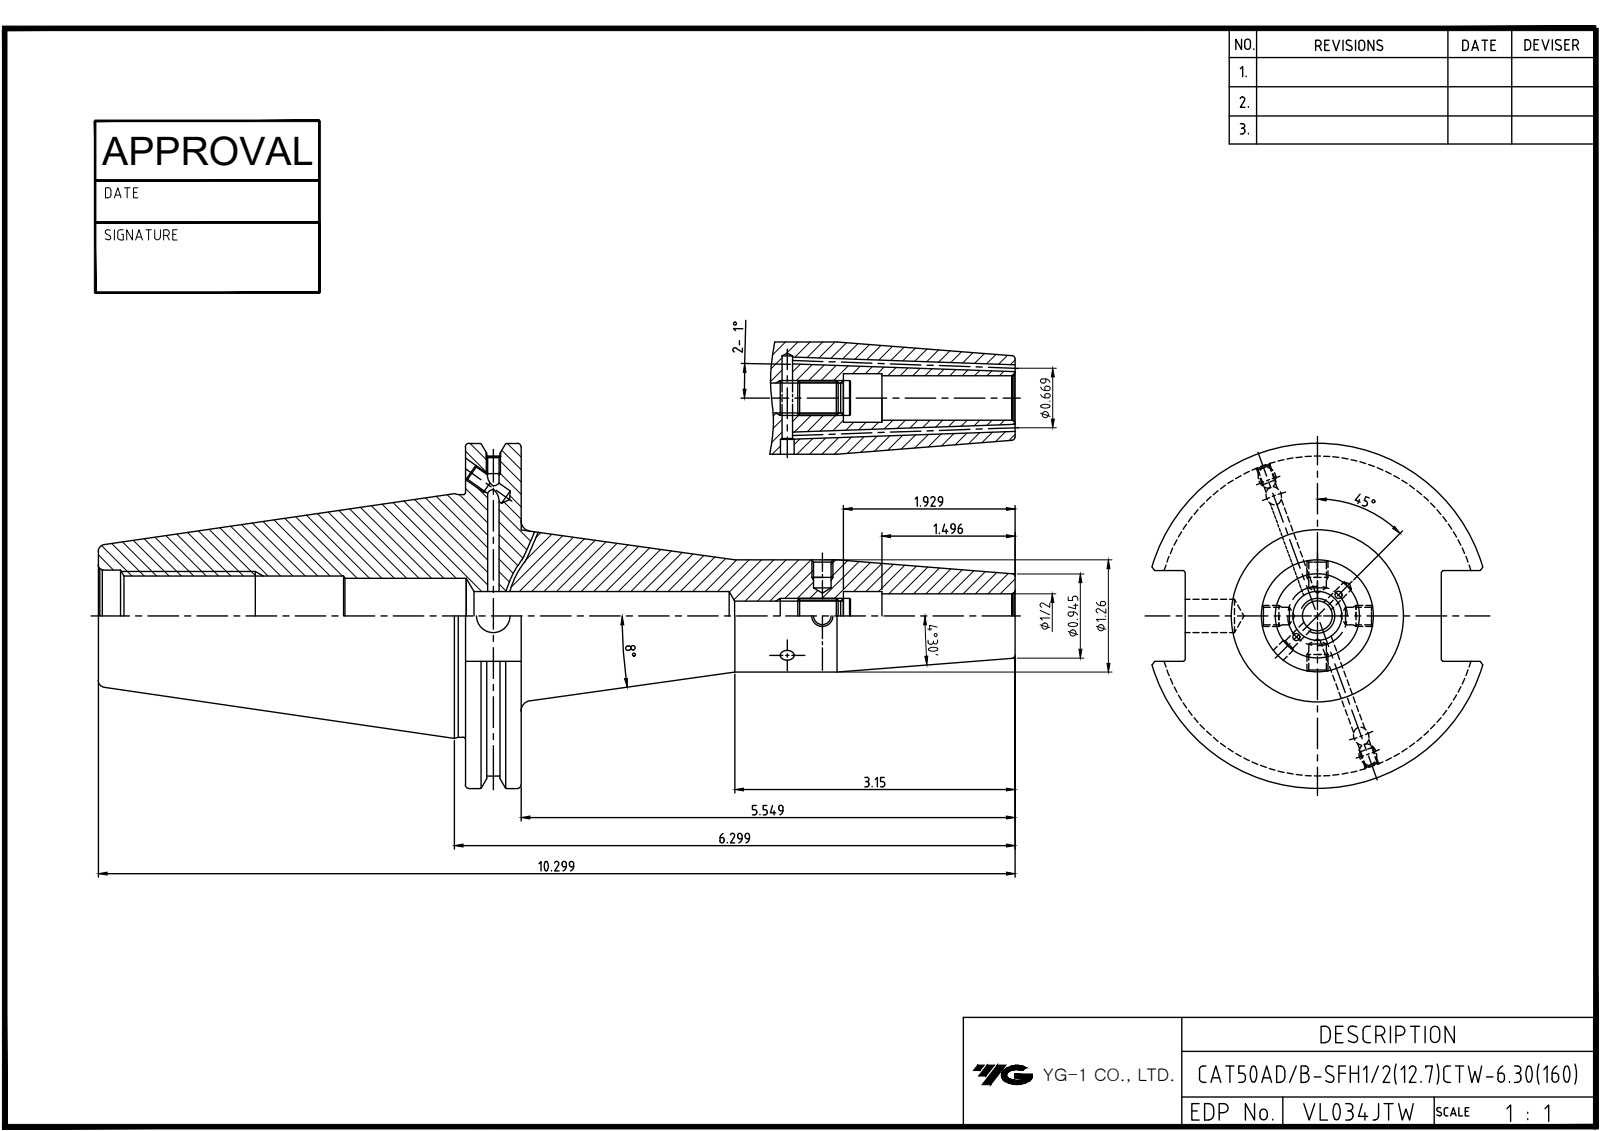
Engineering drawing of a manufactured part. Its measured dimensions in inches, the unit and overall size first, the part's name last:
Units: inches
Overall size (bounding box): 10.305 × 3.875 × 3.718
Round holes (diameter × count): ⌀0.375 ×1, ⌀0.394 ×1, ⌀0.5 ×1, ⌀0.547 ×1, ⌀0.551 ×1, ⌀0.807 ×1, ⌀0.827 ×1, ⌀0.945 ×1, ⌀0.984 ×1, ⌀1.008 ×1
Round bosses / shafts (diameter × count): ⌀3.875 ×1, ⌀3.594 ×1, ⌀2.726 ×1, ⌀1.26 ×1
Main face-to-face distances: 0.626, 4.13, 4.756, 2.875, 1.012, 10.305, 6.175, 5.549, 4.37, 0.24
Volume: 26.97 in³ · Surface area: 102.2 in²
Bodies: 1 solid, 102 faces (30 planar, 30 cylindrical, 42 other)
Part name (STEP PRODUCT): CAT50_SHANK_20130708
STEP written by: CREO PARAMETRIC BY PTC INC, 2018500 (CONFIG_CONTROL_DESIGN)
